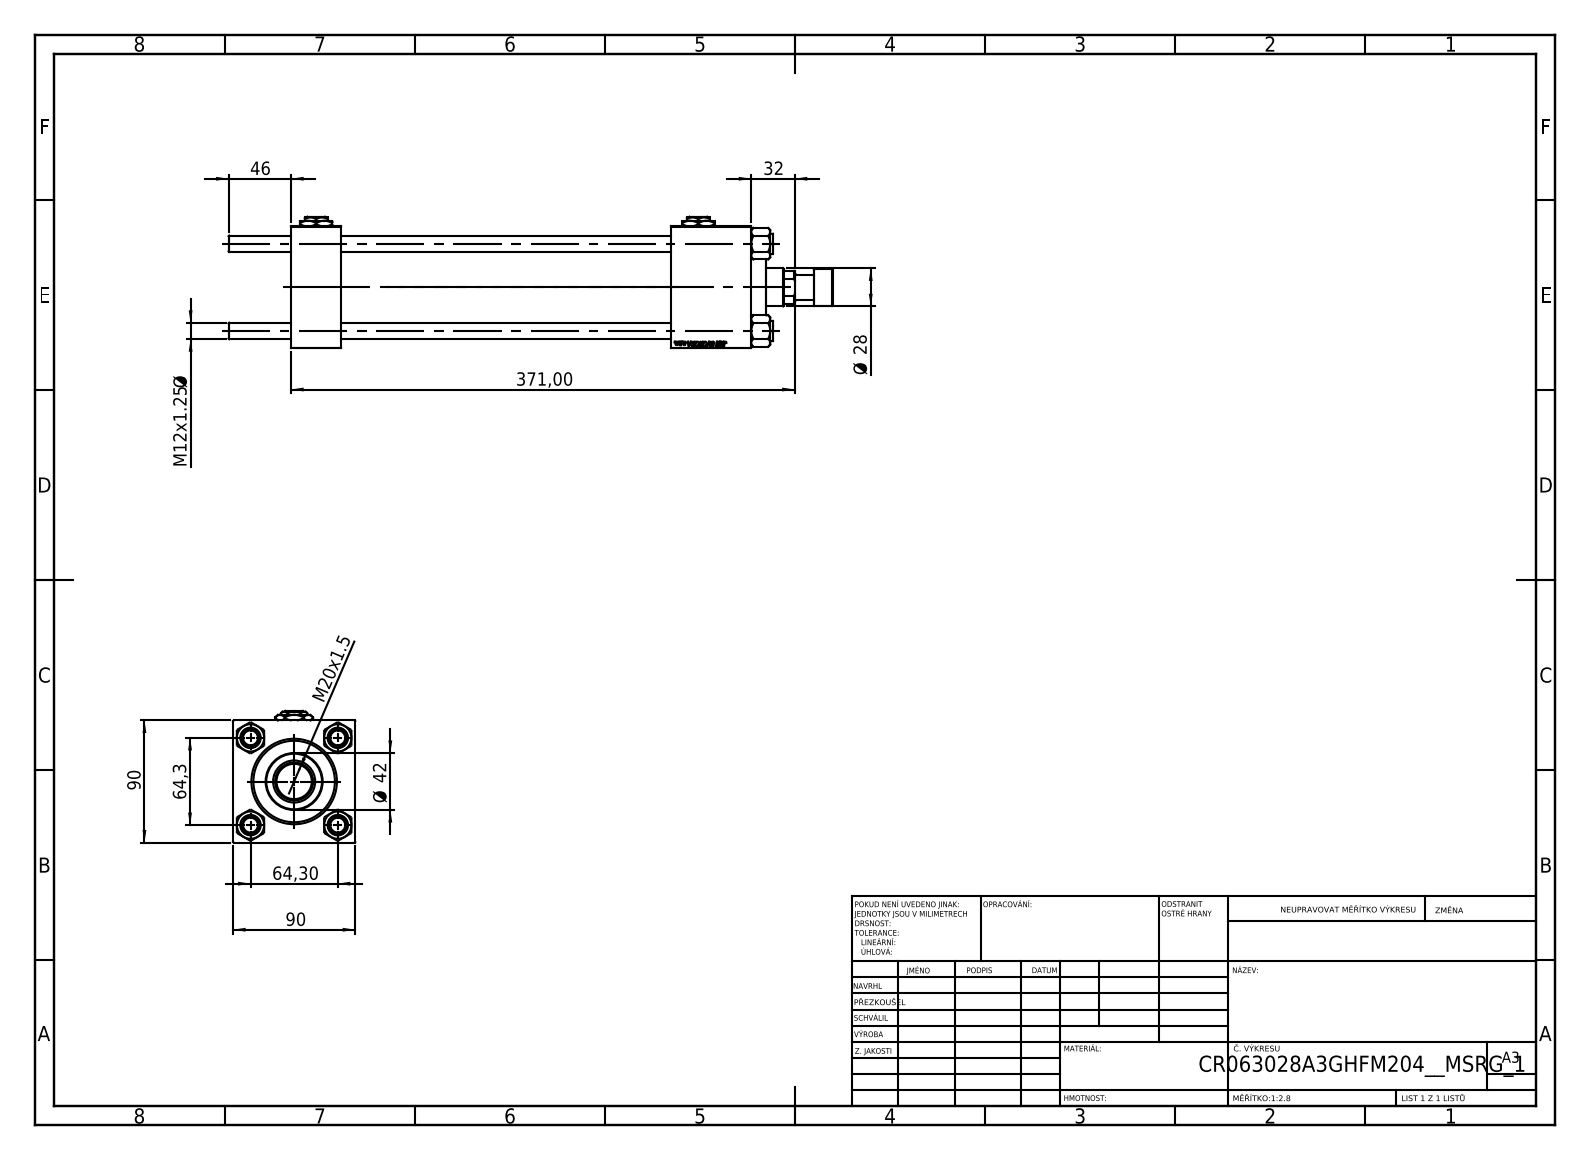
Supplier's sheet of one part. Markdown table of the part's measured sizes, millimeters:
| quantity | value |
| --- | --- |
| part name | V215_VC_A; V215CR_ROD_END_F; CR025_012_A_0_G_A_G_M_020_+#_##_TYCINKA; Zatka_pro_OIL_PORT (+3 more) |
| STEP written by | SolidWorks 2019 (CONFIG_CONTROL_DESIGN) |
| units | millimeters |
| bodies | 14 solids, 1247 faces (571 planar, 92 cylindrical, 584 other) |
| overall size | 445 × 97 × 90 |
| volume | 1 297 000 mm³ |
| surface area | 323 542 mm² |
| round holes (diameter × count) | 12 × 4, 7 × 2, 20.96 × 2, 30 × 2, 18.5 × 1, 28 × 1, 31 × 1, 50 × 1, 60 × 1, 63 × 1 |
| round bosses / shafts (diameter × count) | 15 × 4, 69 × 1, 42 × 1, 27 × 1, 18 × 1 |
| main face-to-face distances | 90, 37, 339, 302, 59, 280, 243, 310.3, 273.3, 30.3 |
| hole center spacings | 45.47, 64.3, 90.93, 281.5 |
